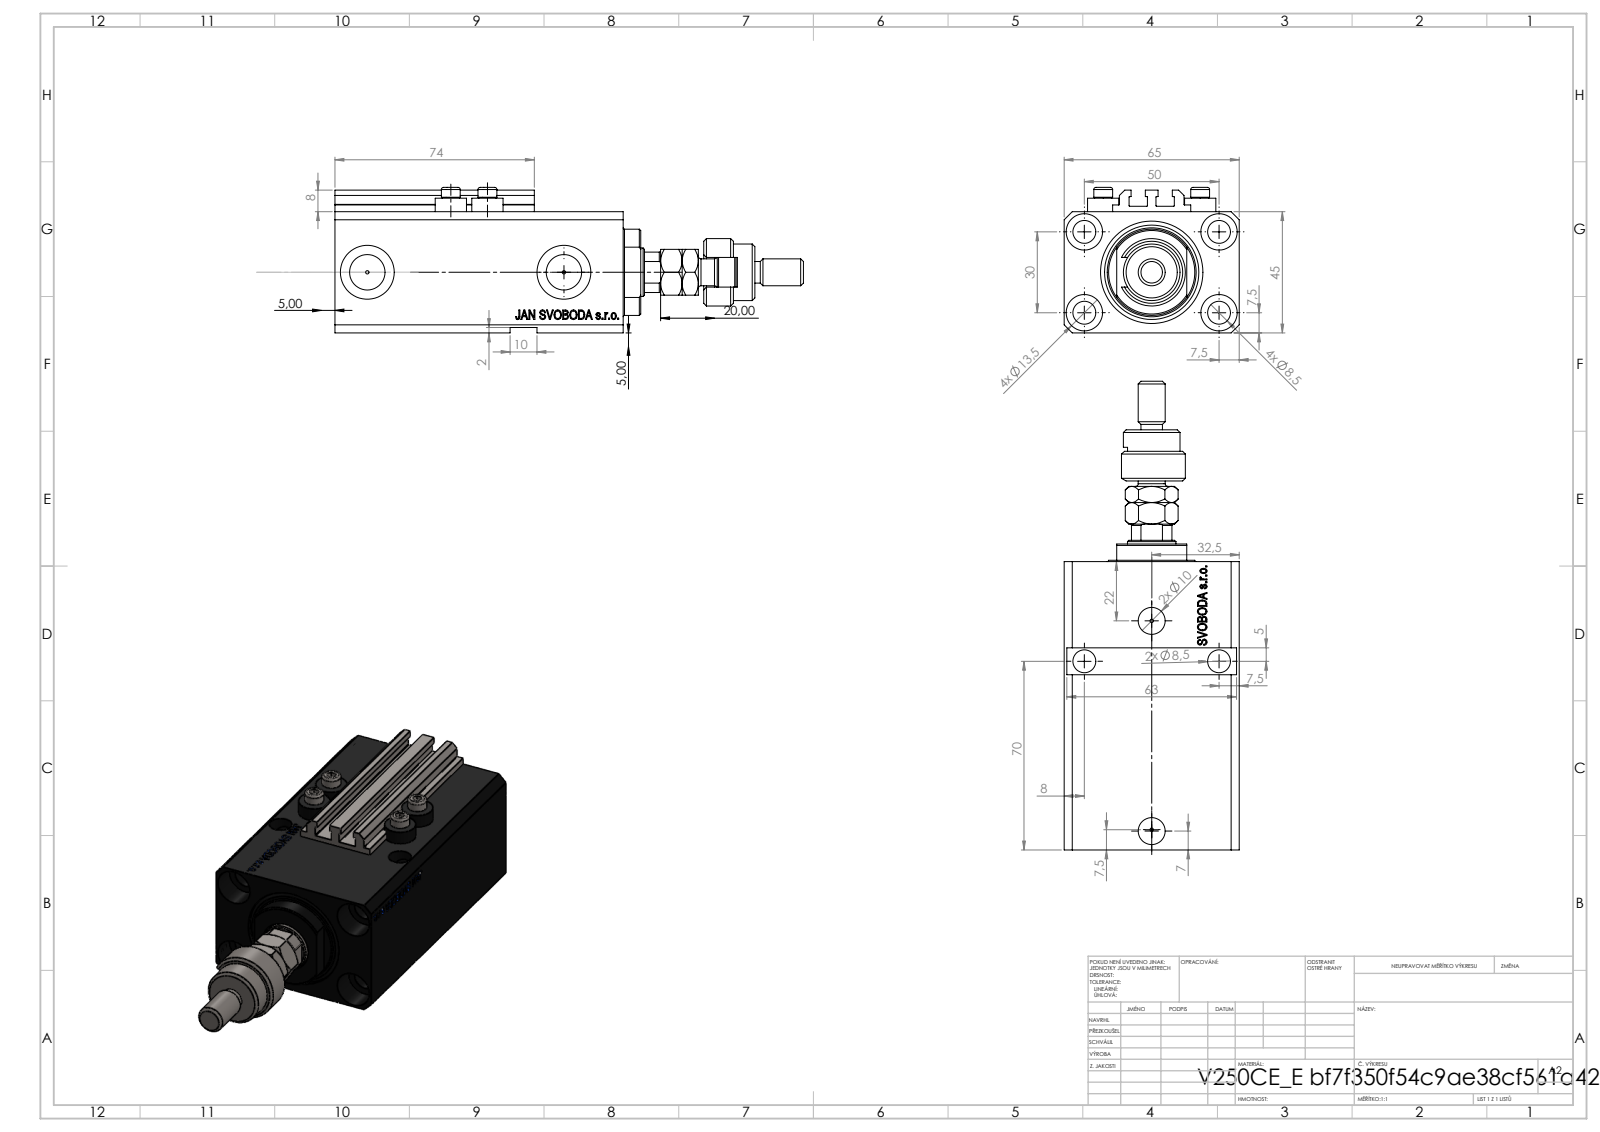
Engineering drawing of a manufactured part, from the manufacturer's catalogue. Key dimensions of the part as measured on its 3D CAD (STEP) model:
Part name (STEP PRODUCT): V250CE_C_VCP; FEMALE_PART_FOR_DFA; V250CE_E_Body; ALLEN BOLT V250CE (+2 more)
STEP written by: SolidWorks 2019 (CONFIG_CONTROL_DESIGN)
Units: millimetres
Bodies: 10 solids, 1172 faces (539 planar, 159 cylindrical, 474 other)
Overall size (bounding box): 174 × 65 × 54
Volume: 285 194 mm³ · Surface area: 82 321 mm²
Round holes (diameter × count): ⌀8.5 ×9, ⌀1.25 ×4, ⌀4 ×4, ⌀13.5 ×4, ⌀10 ×2, ⌀13.16 ×2, ⌀20 ×2, ⌀18 ×1, ⌀38 ×1
Round bosses / shafts (diameter × count): ⌀11.6 ×4, ⌀7 ×4, ⌀25 ×1, ⌀21 ×1, ⌀16 ×1, ⌀10 ×1, ⌀8 ×1
Partial cylindrical surfaces — rounded edges, fillets, slot ends (radius × count): R0.2 ×10, R5.5 ×1, R8.5 ×1, R8.75 ×1, R16 ×1
Main face-to-face distances: 45, 65, 14, 2, 93, 47, 107, 2.5, 3, 10
Hole centre spacings: 29.15, 50, 13.6, 14.76, 15.12, 27.51, 27.89, 30
